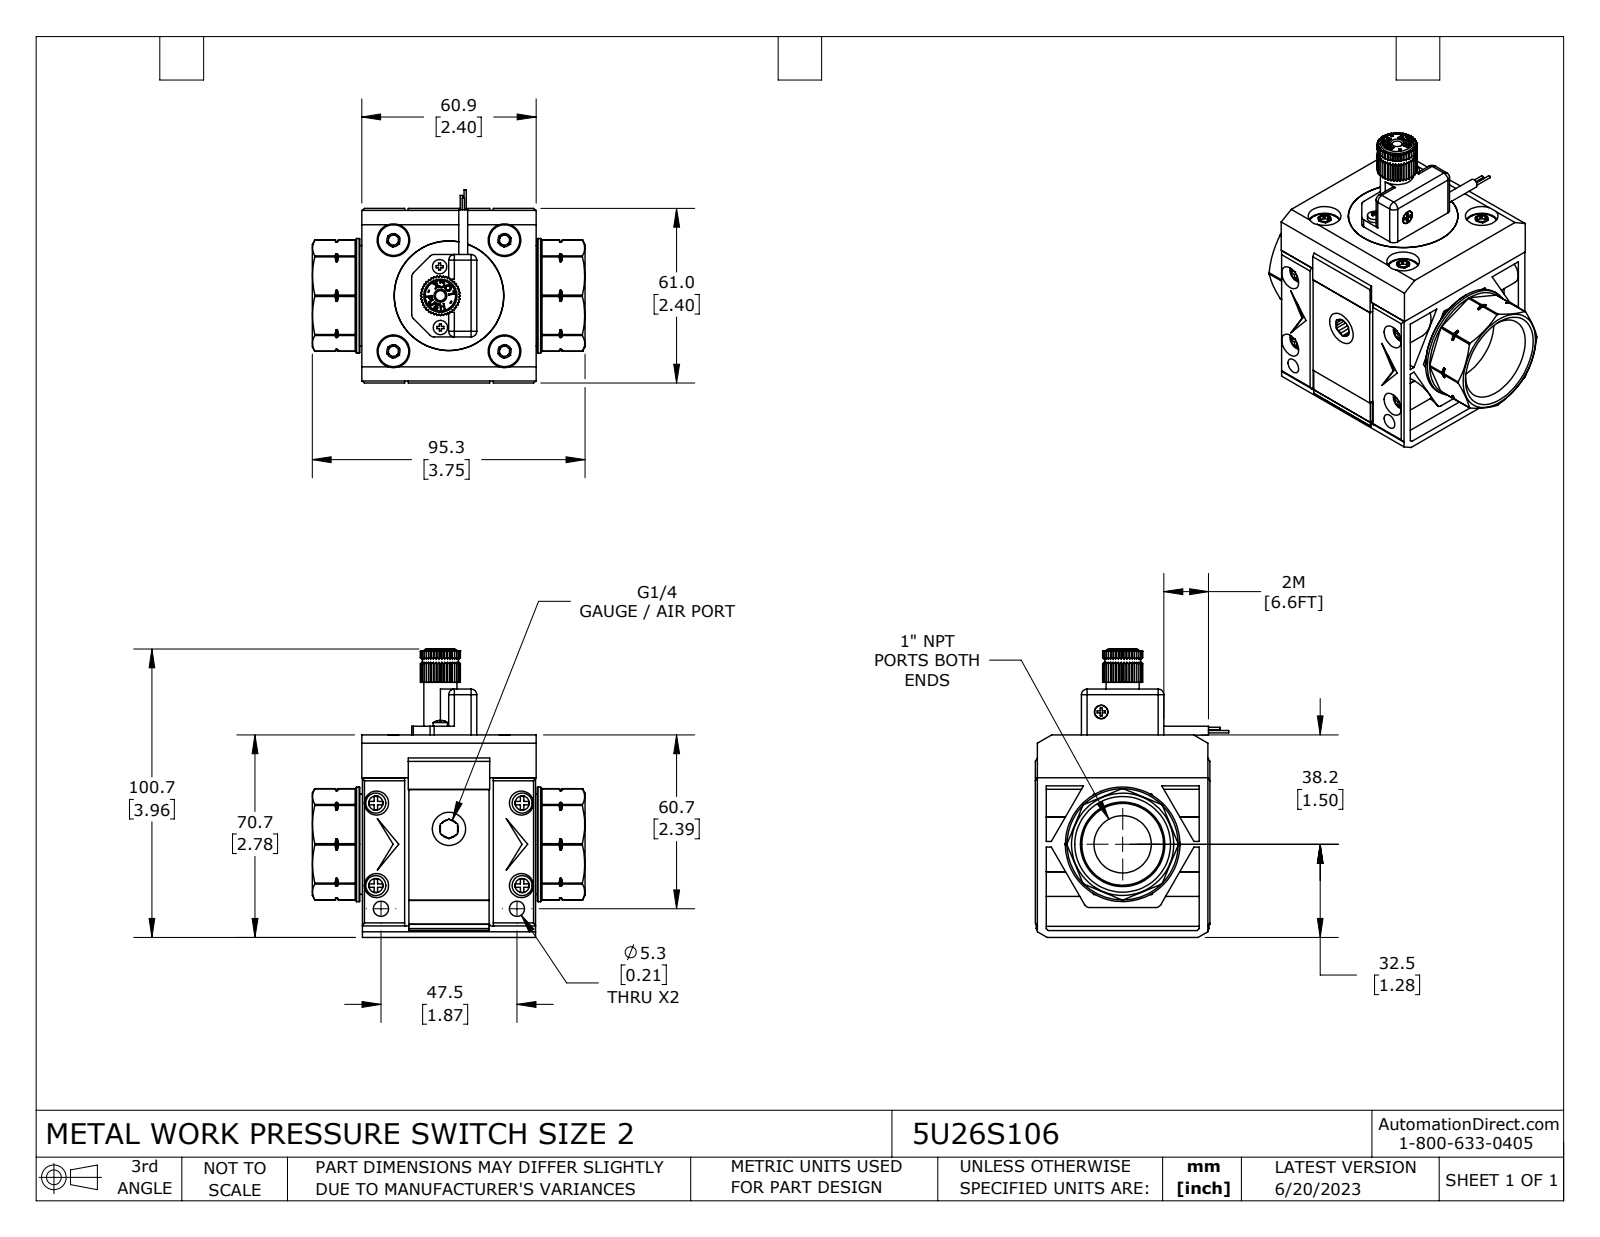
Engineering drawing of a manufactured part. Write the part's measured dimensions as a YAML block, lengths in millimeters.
part_name: "5U26S106"
step_written_by: "SolidWorks 2021 (CONFIG_CONTROL_DESIGN)"
units: millimeters
bodies: {solids: 13, faces: 1387, planar: 702, cylindrical: 409, other: 276}
overall_size: [100.7, 95.3, 67.5]
volume: 219100
surface_area: 78520
round_holes:
  - {diameter: 3.3, count: 4}
  - {diameter: 4.2, count: 4}
  - {diameter: 8.4, count: 4}
  - {diameter: 11.4, count: 4}
  - {diameter: 5.3, count: 2}
  - {diameter: 1.8, count: 1}
  - {diameter: 11.6, count: 1}
  - {diameter: 20, count: 1}
  - {diameter: 31.8, count: 1}
  - {diameter: 38.3, count: 1}
round_bosses_or_shafts:
  - {diameter: 7, count: 4}
  - {diameter: 4.8, count: 4}
  - {diameter: 3.8, count: 4}
  - {diameter: 0.8, count: 3}
  - {diameter: 5, count: 2}
  - {diameter: 40, count: 1}
  - {diameter: 38.2, count: 1}
  - {diameter: 35, count: 1}
partial_cylinders:
  - {radius: 0.3, count: 28}
  - {radius: 2, count: 14}
  - {radius: 1.8, count: 4}
  - {radius: 4.9, count: 4}
  - {radius: 6.1, count: 2}
  - {radius: 0.2, count: 1}
  - {radius: 0.2, count: 1}
  - {radius: 0.2, count: 1}
face_to_face_distances: [60.7, 2.4, 55.7, 53.3, 0.7, 7.6, 61, 45.7, 70.7, 68.3]
hole_center_spacings: [27.4, 38.8, 8.3, 26.8, 28.8, 32.1, 36.7, 36.9]
